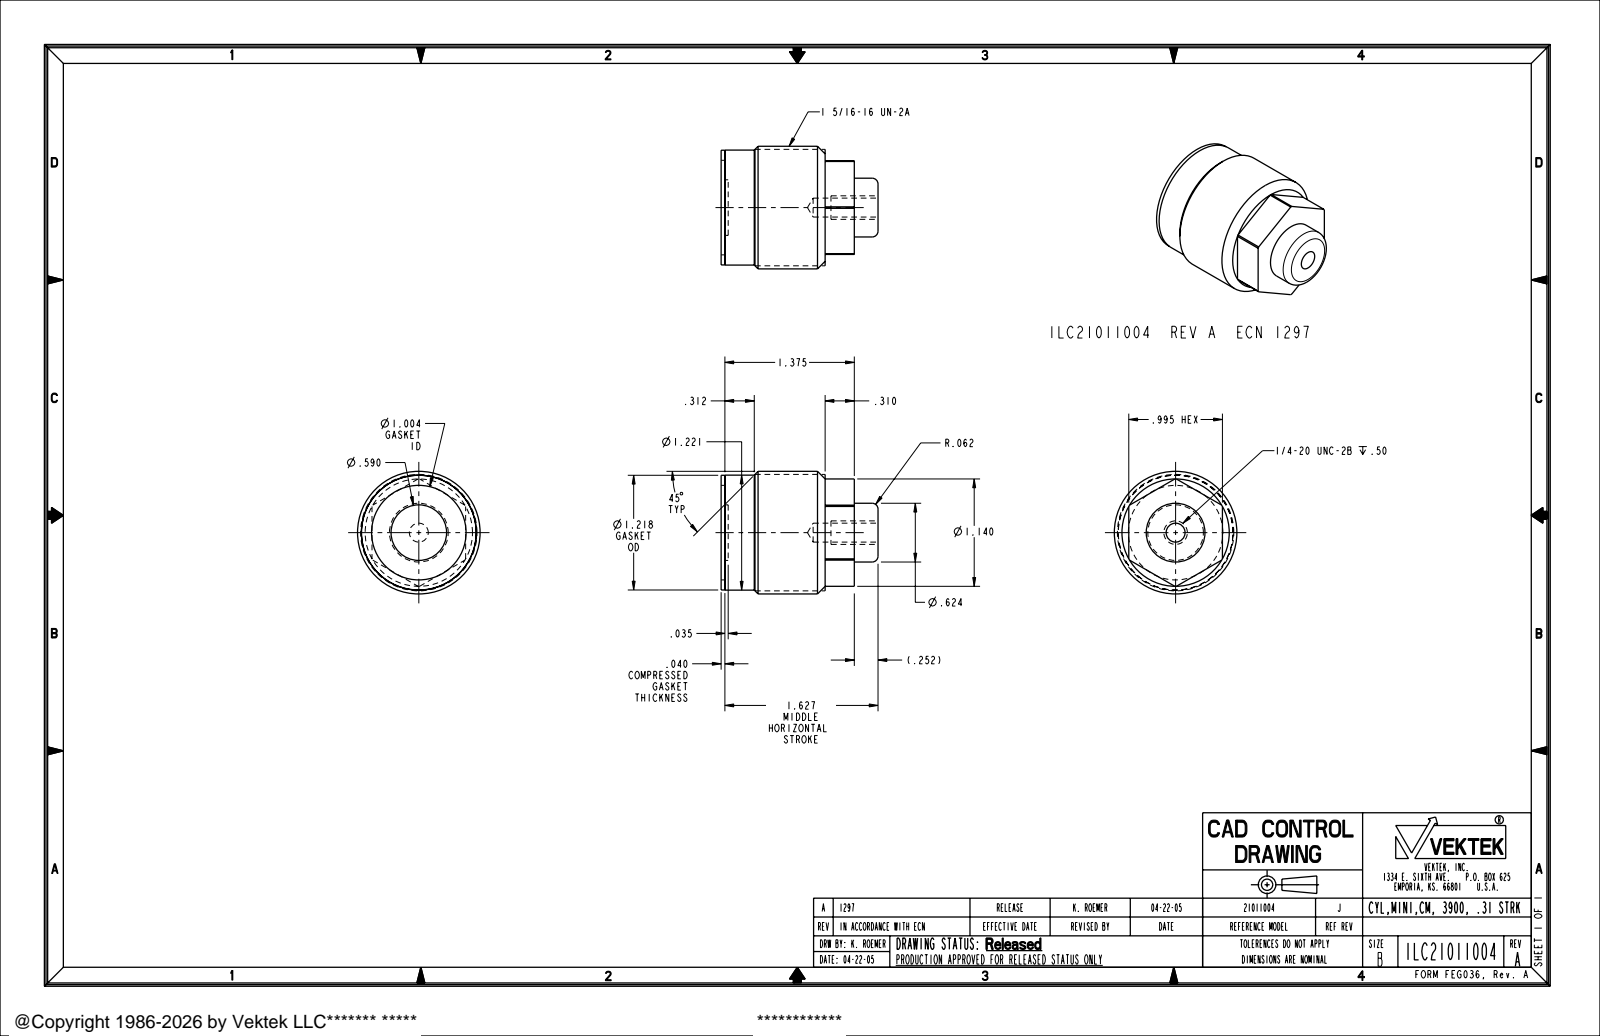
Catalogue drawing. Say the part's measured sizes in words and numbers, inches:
The part is named "ILC21011004". Its 3-D file was written by "PRO/ENGINEER BY PARAMETRIC TECHNOLOGY CORPORATION, 2004290 (AUTOMOTIVE_DESIGN_CC2)". It is 2 solids with 52 faces: 20 planar, 24 cylindrical and 8 other. Overall it measures 1.667 by 1.302 by 1.302 inches. Its volume is 1.675 cubic inches and its surface area 14.17 square inches. Round holes: 1 of diameter 0.201, 1 of diameter 0.59, 1 of diameter 1.004. Round bosses or shafts: 1 of diameter 1.302, 1 of diameter 1.237, 1 of diameter 1.221, 1 of diameter 1.218, 1 of diameter 0.624, 1 of diameter 0.25. Partial cylindrical surfaces (rounded edges, fillets, slot ends): 1 of radius 0.57. The main face-to-face distances are 1.065, 1.375, 0.31, 0.995, 0.039, 0.04, 1.105, 1.415, 1.066, 1.376.
